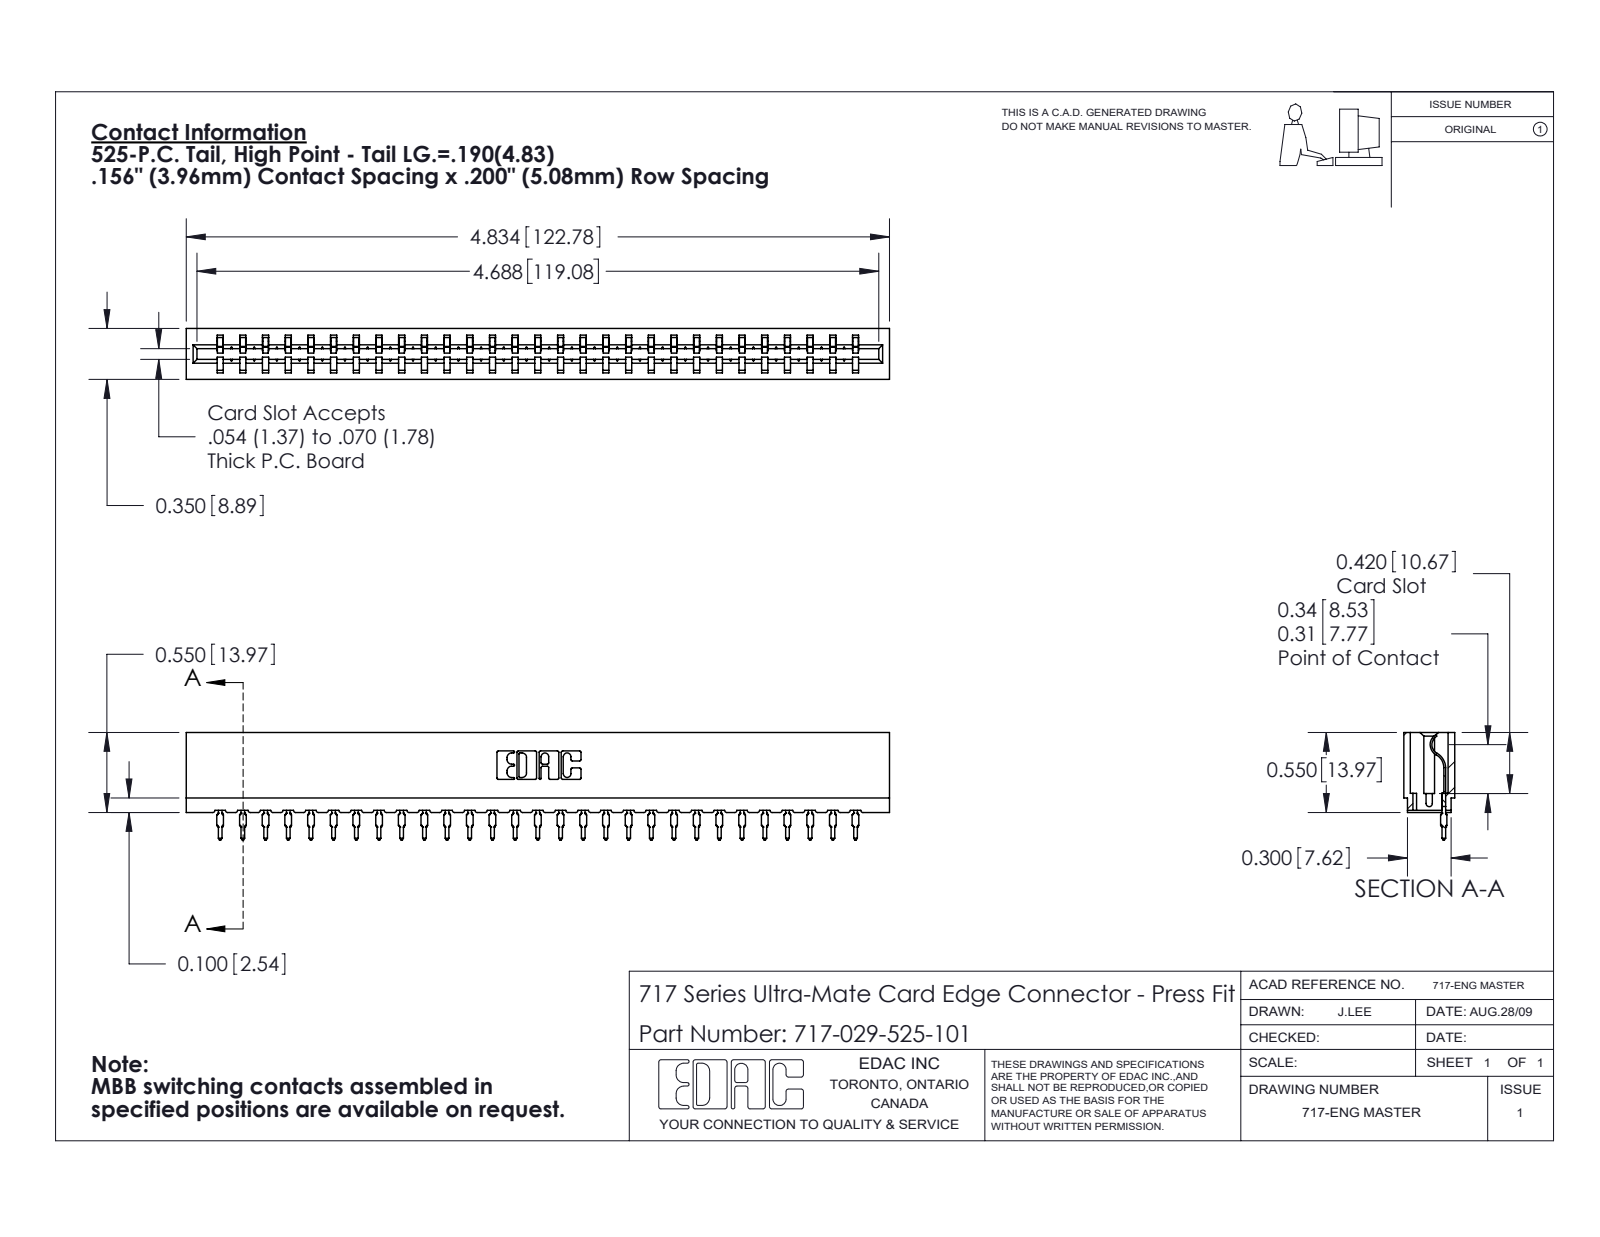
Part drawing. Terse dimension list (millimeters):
name: 717 Part_Insulator Option - 06; 717-029-525-101; 745-292-001_525
written by: SolidWorks 2020 (CONFIG_CONTROL_DESIGN)
unit: mm
bodies: 30 solids, 3371 faces (2026 planar, 591 cylindrical, 754 other)
size: 122.8 × 18.8 × 8.9
volume: 10 400 mm³; area: 14 380 mm²
rounds: 58× R0.4, 58× R0.5, 22× R0.3, 6× R0.2, 6× R0.8, 4× R0.1, 4× R0.3, 3× R0.7
face distances: 5.4, 3.5, 8.9, 1.9, 4, 1.1, 7.7, 2.4, 4.2, 0.6
